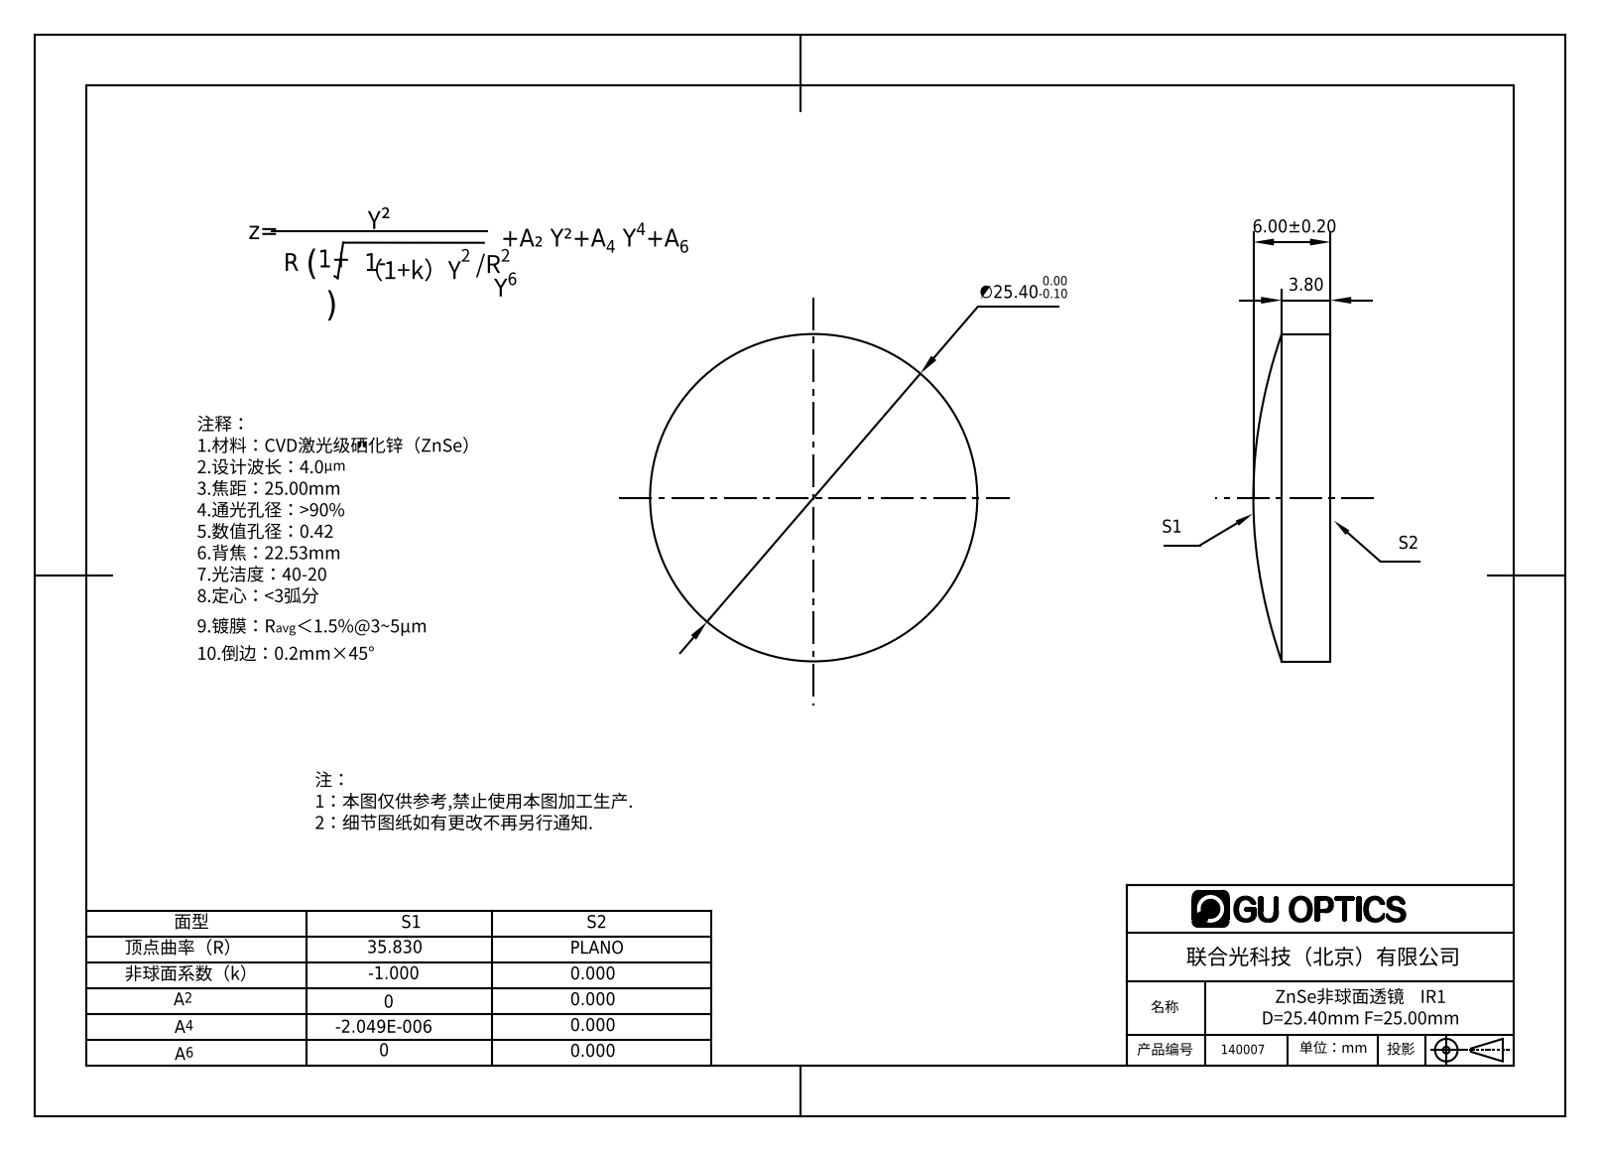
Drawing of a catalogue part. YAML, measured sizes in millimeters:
part_name: "140007"
step_written_by: "SolidWorks 2020 (CONFIG_CONTROL_DESIGN)"
units: millimeters
bodies: {solids: 1, faces: 5, planar: 1, cylindrical: 2, other: 2}
overall_size: [25.4, 25.4, 6]
volume: 2479
surface_area: 1331
round_bosses_or_shafts:
  - {diameter: 25.4, count: 1}
